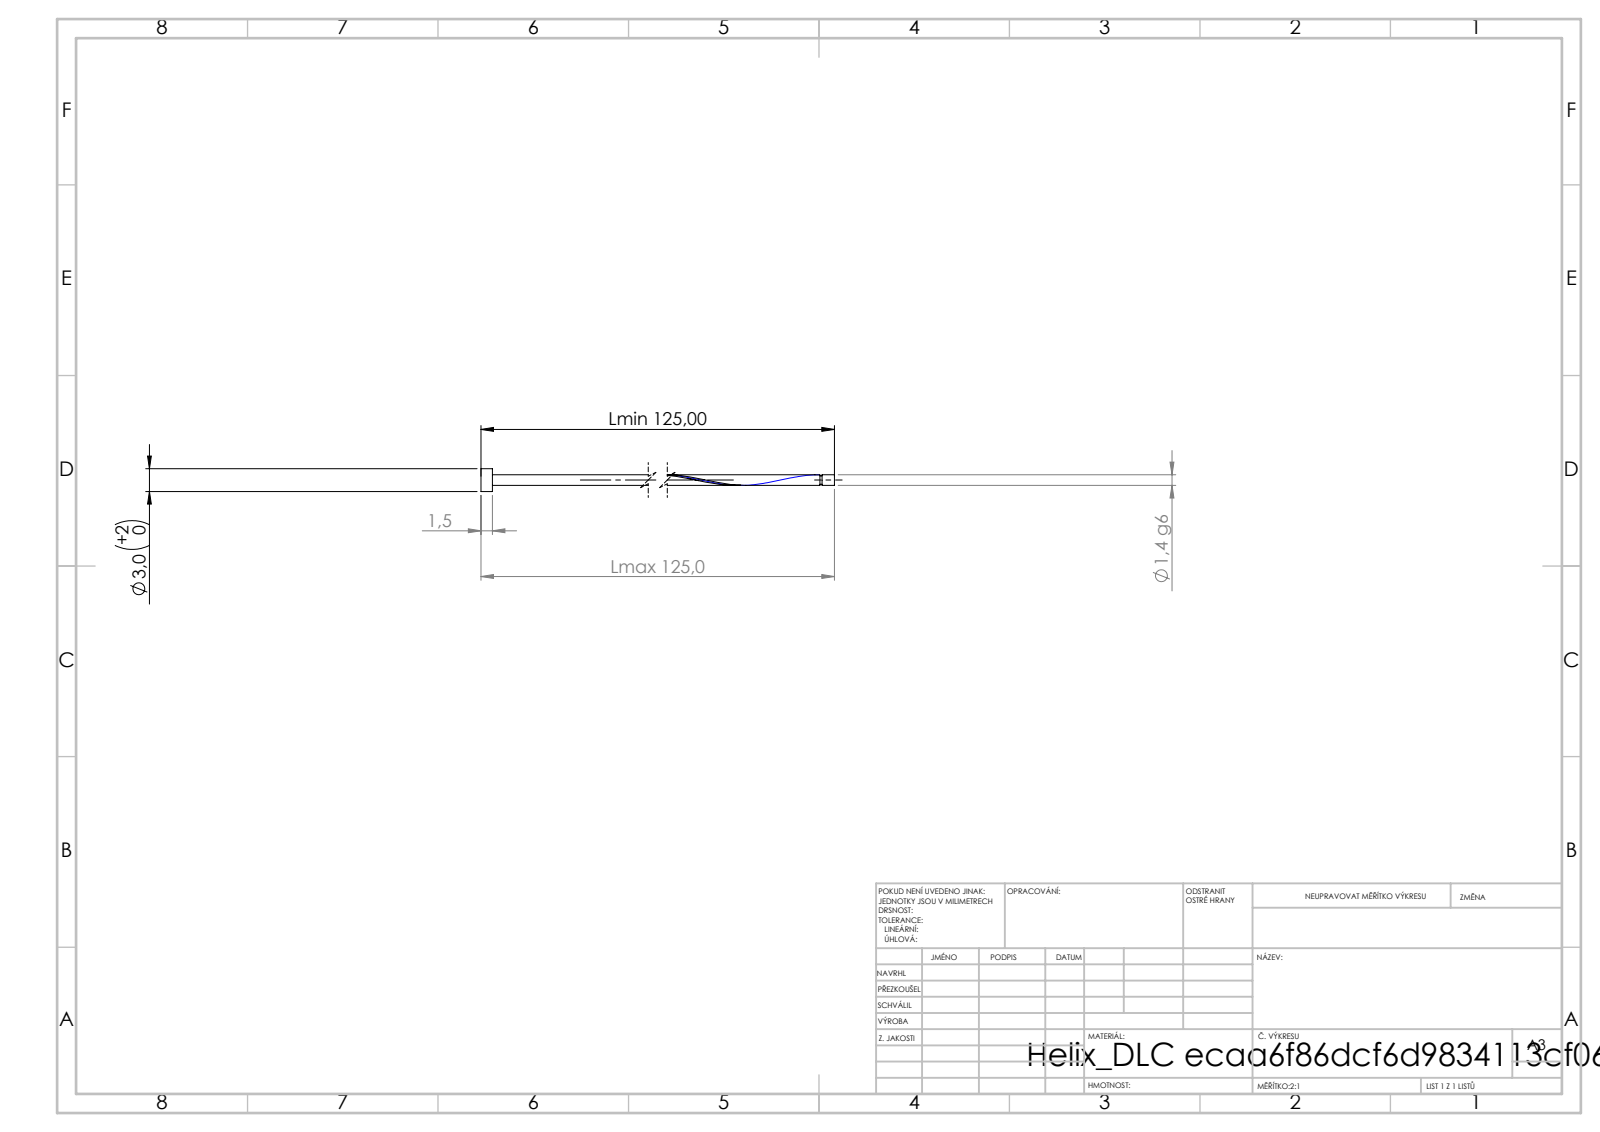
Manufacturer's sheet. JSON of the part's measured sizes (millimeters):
{"step_written_by": "SolidWorks 2019 (CONFIG_CONTROL_DESIGN)", "units": "millimeters", "bodies": {"solids": 1, "faces": 16, "planar": 6, "cylindrical": 9, "other": 1}, "overall_size": [125, 3, 3], "volume_mm3": 242, "surface_area_mm2": 764, "round_bosses_or_shafts": [[3, 1], [1.4, 1], [1.12, 1]], "face_to_face_distances": [1.5, 125, 123.5, 123.38, 121.88, 1.62, 123.1, 121.6, 1.9, 60.6]}
